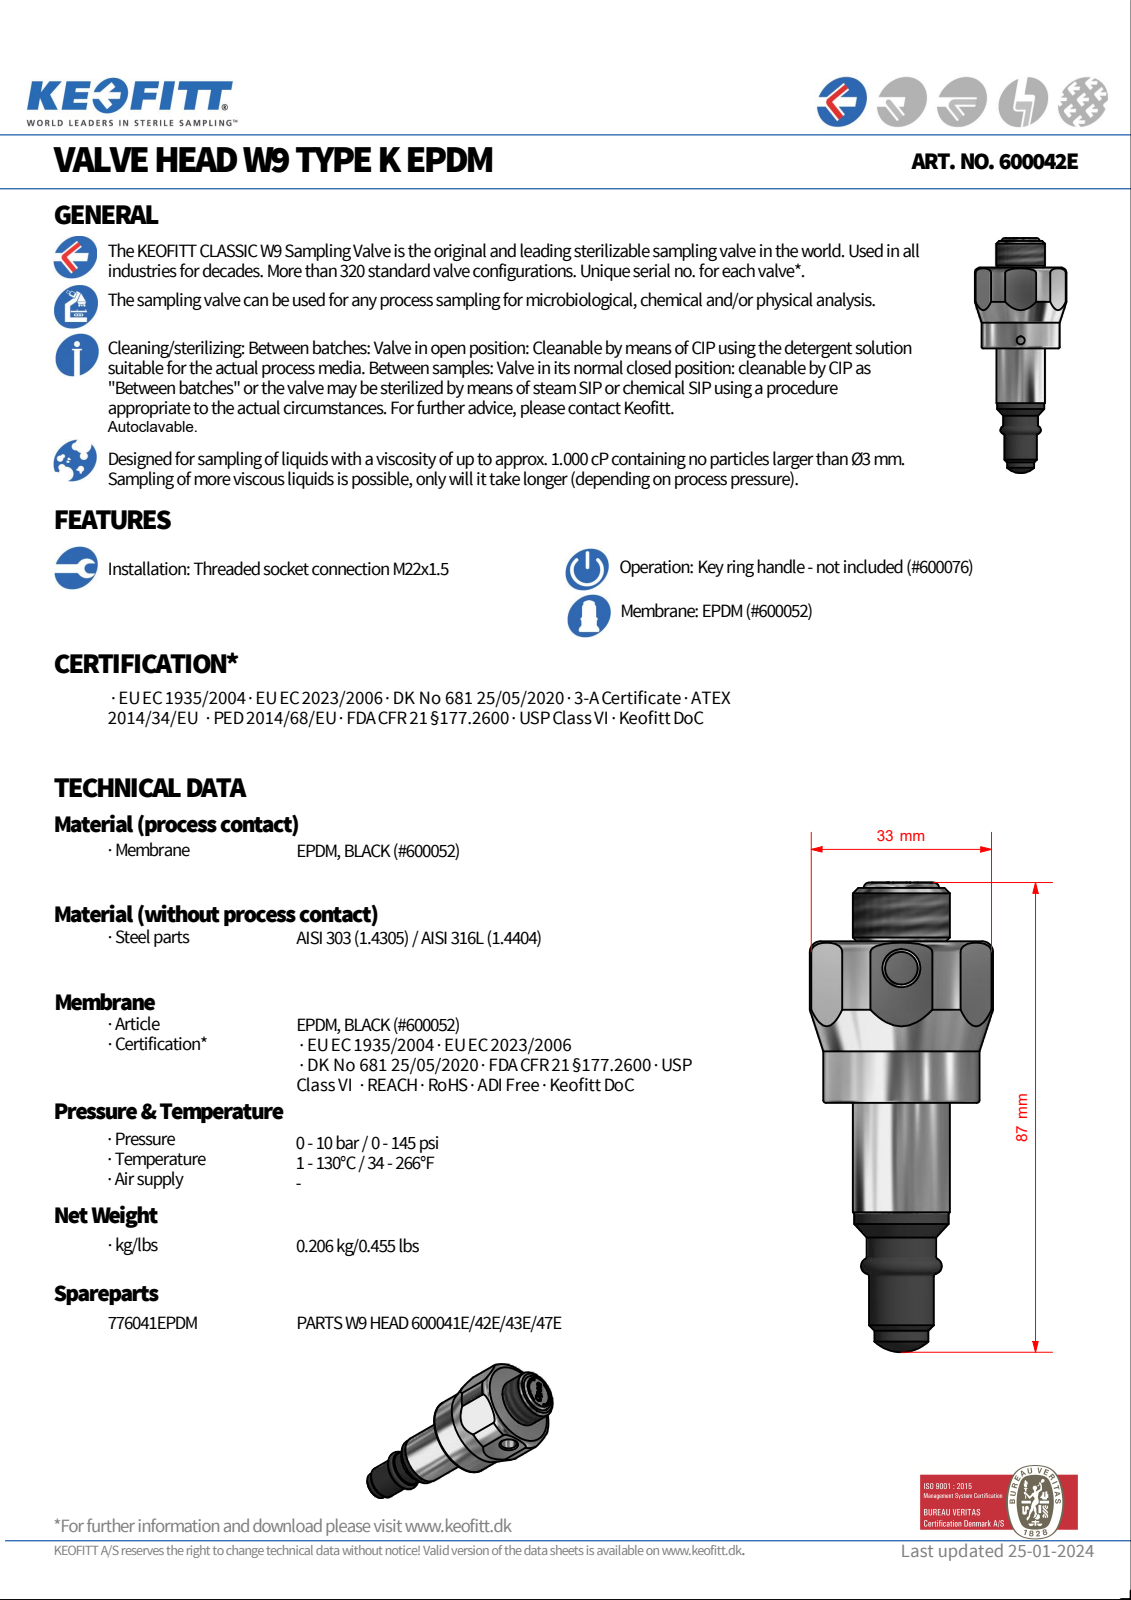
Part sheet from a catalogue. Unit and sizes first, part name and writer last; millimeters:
Units: millimetres
Overall size (bounding box): 87.2 × 34 × 32
Round bosses / shafts (diameter × count): ⌀29 ×1, ⌀18 ×1, ⌀17.5 ×1, ⌀14 ×1, ⌀12.9 ×1, ⌀12 ×1, ⌀10 ×1
Partial cylindrical surfaces — rounded edges, fillets, slot ends (radius × count): R5.15 ×1, R5.55 ×1, R17 ×1
Main face-to-face distances: 32, 30, 17.8, 47.8, 60, 42.2, 12.2, 18, 48, 60.2
Volume: 33 729 mm³ · Surface area: 7 549 mm²
Bodies: 1 solid, 283 faces (122 planar, 19 cylindrical, 142 other)
Part name (STEP PRODUCT): 600042E
STEP written by: Autodesk Inventor 2024 (AUTOMOTIVE_DESIGN)
